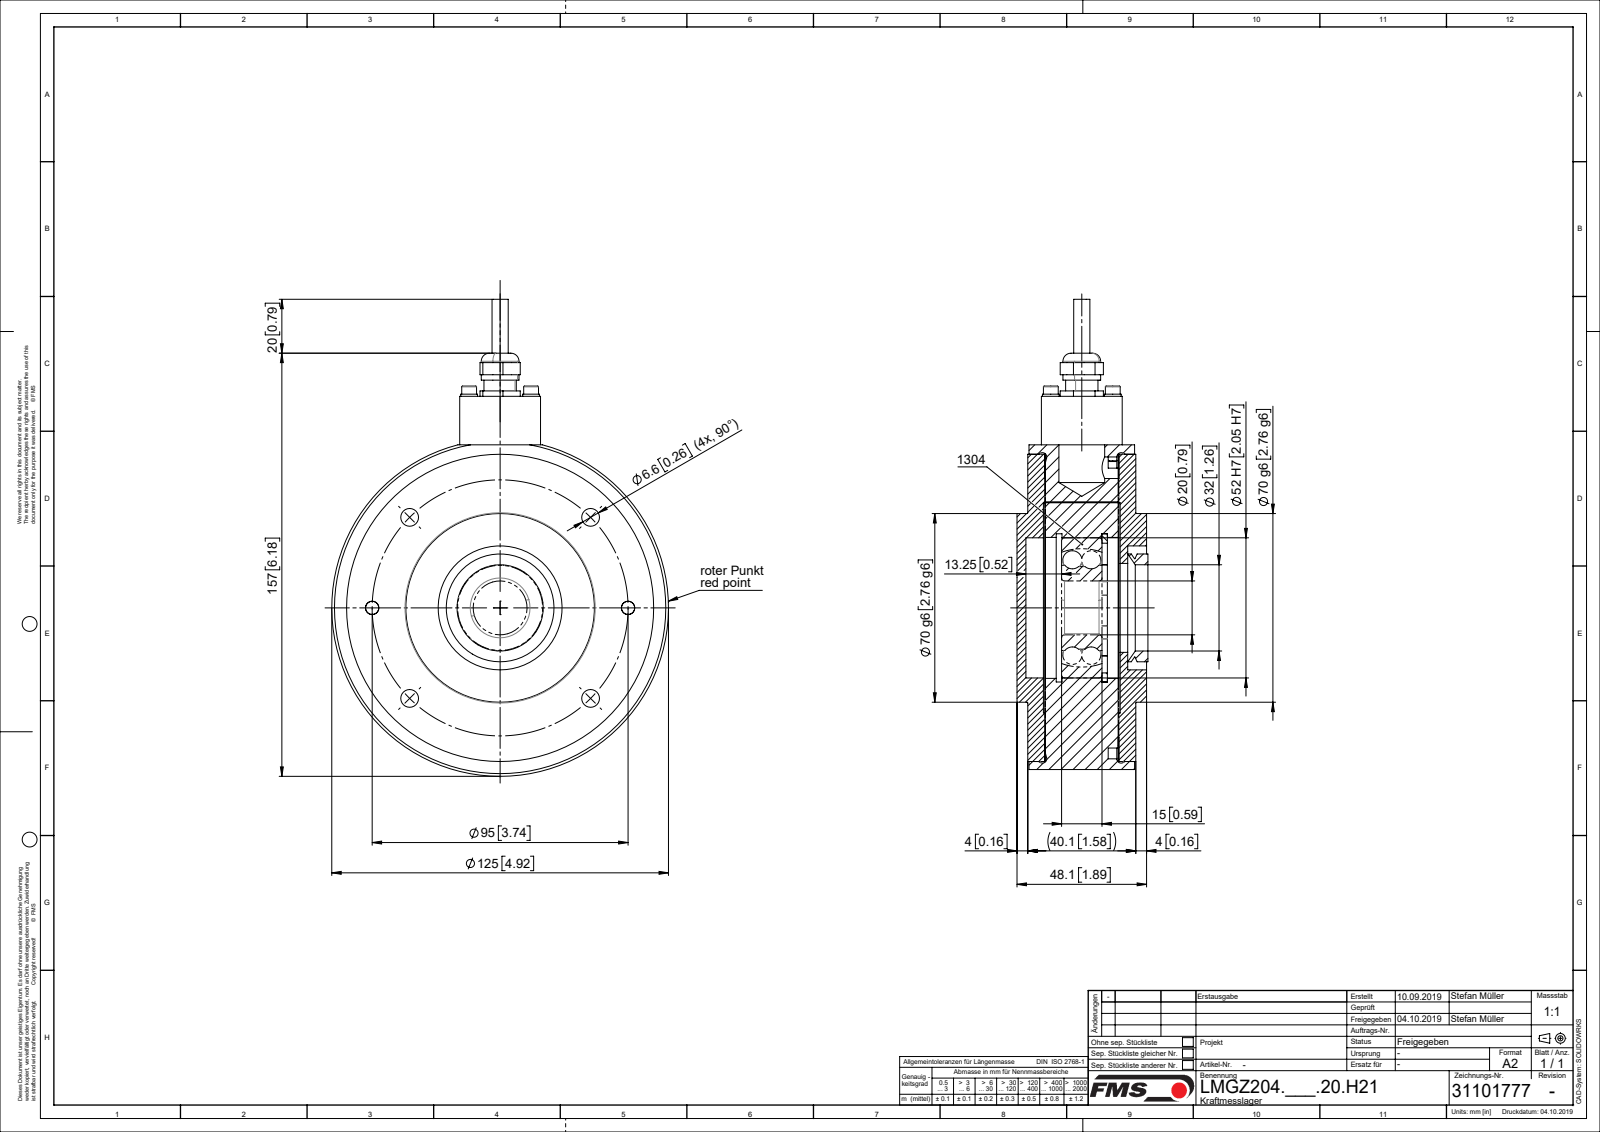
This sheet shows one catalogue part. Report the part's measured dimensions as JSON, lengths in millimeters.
{"part_name": "ZEICHNUNG4; ZEICHNUNG7; L50059; L4832404 (+8 more)", "step_written_by": "Mechanical Desktop 2009 (CONFIG_CONTROL_DESIGN)", "units": "millimeters", "bodies": {"solids": 20, "faces": 375, "planar": 111, "cylindrical": 212, "other": 52}, "overall_size": [157, 125, 48.1], "volume_mm3": 462503, "surface_area_mm2": 138353, "round_holes": [[6.6, 6], [2.6, 4], [3.2, 4], [3.4, 4], [5, 2], [11, 2], [6, 1], [11.28, 1], [20, 1], [23, 1], [31, 1], [33, 1]], "round_bosses_or_shafts": [[6.2, 4], [5.5, 4], [3, 4], [10, 2], [6, 2], [125, 1], [114, 1], [70, 1]], "partial_cylinders_radius": [[5, 8], [40.5, 1], [47, 1]], "face_to_face_distances": [27.25, 33.55, 6.3, 6.55, 33.8, 27, 27.5, 4, 10.55, 37.8], "hole_center_spacings": [47.5, 16.26, 23, 36.36, 67.18, 87.77, 32.53, 95.01]}
